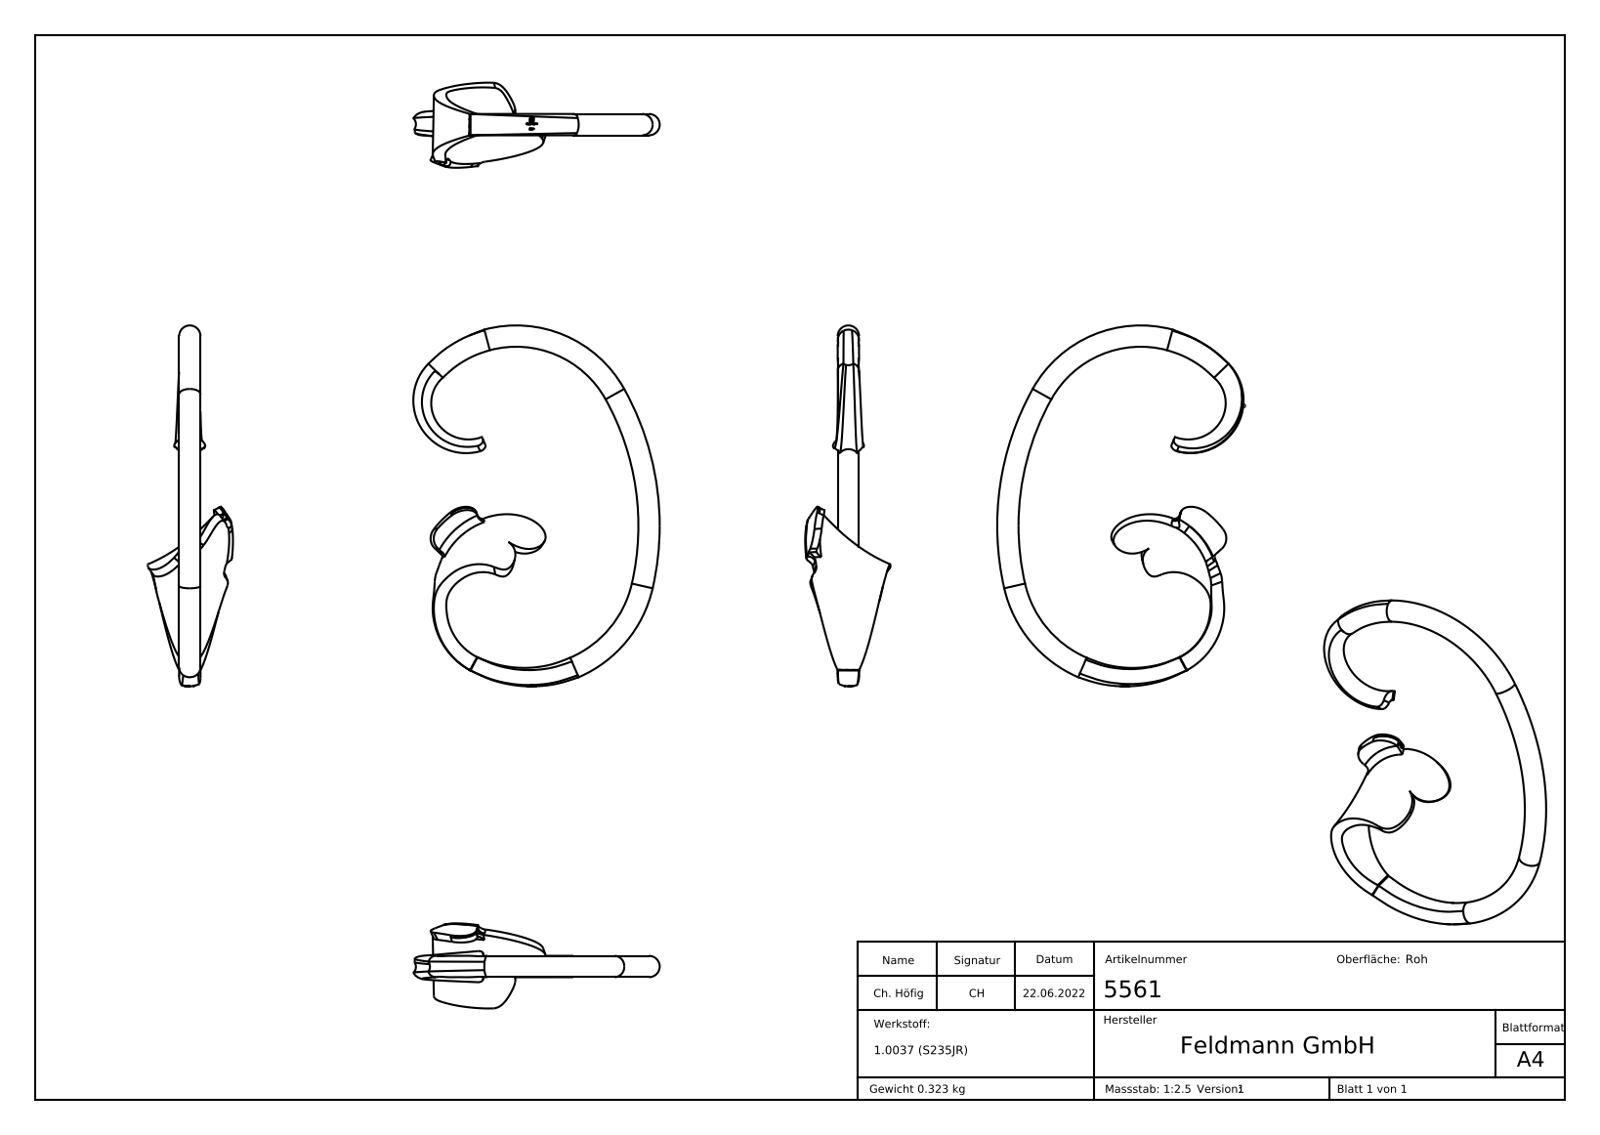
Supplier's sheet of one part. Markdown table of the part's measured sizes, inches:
| quantity | value |
| --- | --- |
| part name | 5561 |
| STEP written by | SolidWorks 2018 (CONFIG_CONTROL_DESIGN) |
| units | inches |
| bodies | 1 solid, 271 faces (101 planar, 0 cylindrical, 170 other) |
| overall size | 6.668 × 4.551 × 1.572 |
| volume | 2.529 in³ |
| surface area | 28.6 in² |
| main face-to-face distances | 0.069, 0.089, 0.019, 0.091, 0.077, 0.019, 0.059, 0.07, 0.048, 0.099 |
